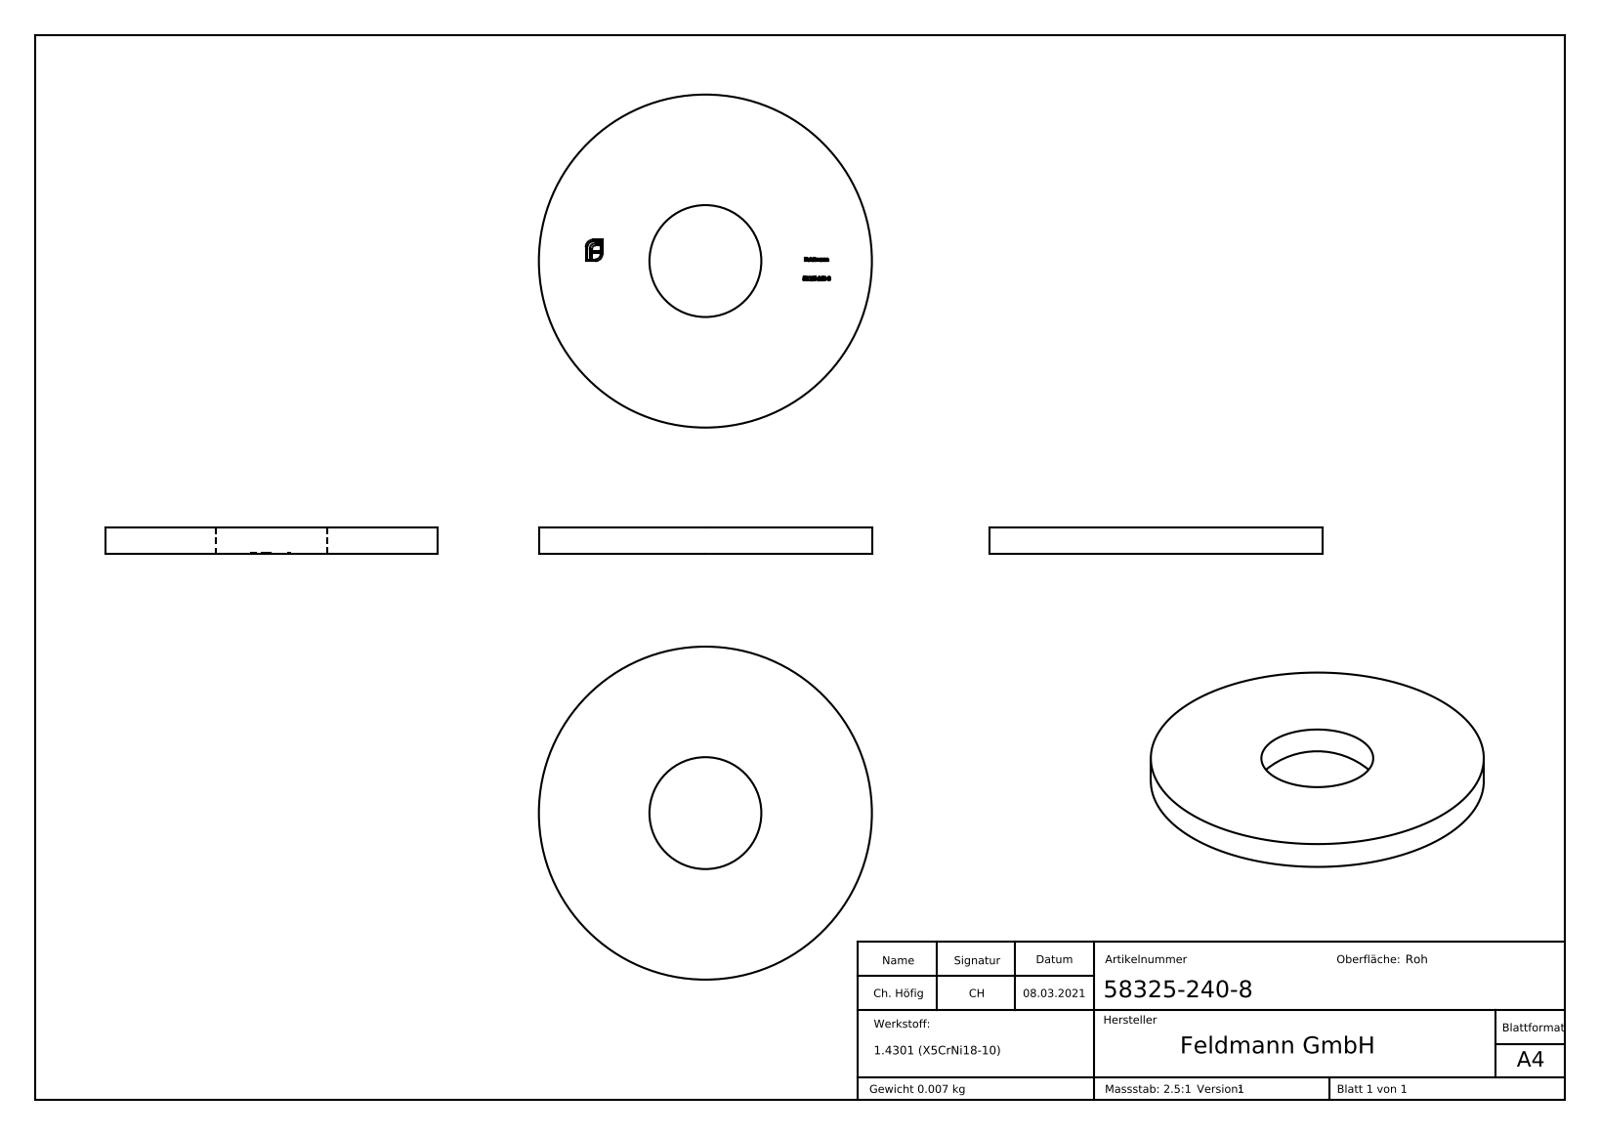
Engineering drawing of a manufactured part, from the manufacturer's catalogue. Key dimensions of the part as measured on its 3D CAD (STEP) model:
Part name (STEP PRODUCT): 58325-240-8
STEP written by: SolidWorks 2018 (CONFIG_CONTROL_DESIGN)
Units: millimetres
Bodies: 1 solid, 310 faces (153 planar, 4 cylindrical, 153 other)
Overall size (bounding box): 25 × 25 × 2
Volume: 871 mm³ · Surface area: 1 084 mm²
Round holes (diameter × count): ⌀8.4 ×1
Round bosses / shafts (diameter × count): ⌀25 ×1
Main face-to-face distances: 2, 1.9, 1.12, 0.65, 1.47, 1.25, 0.89, 0.58, 0.99, 1.44
